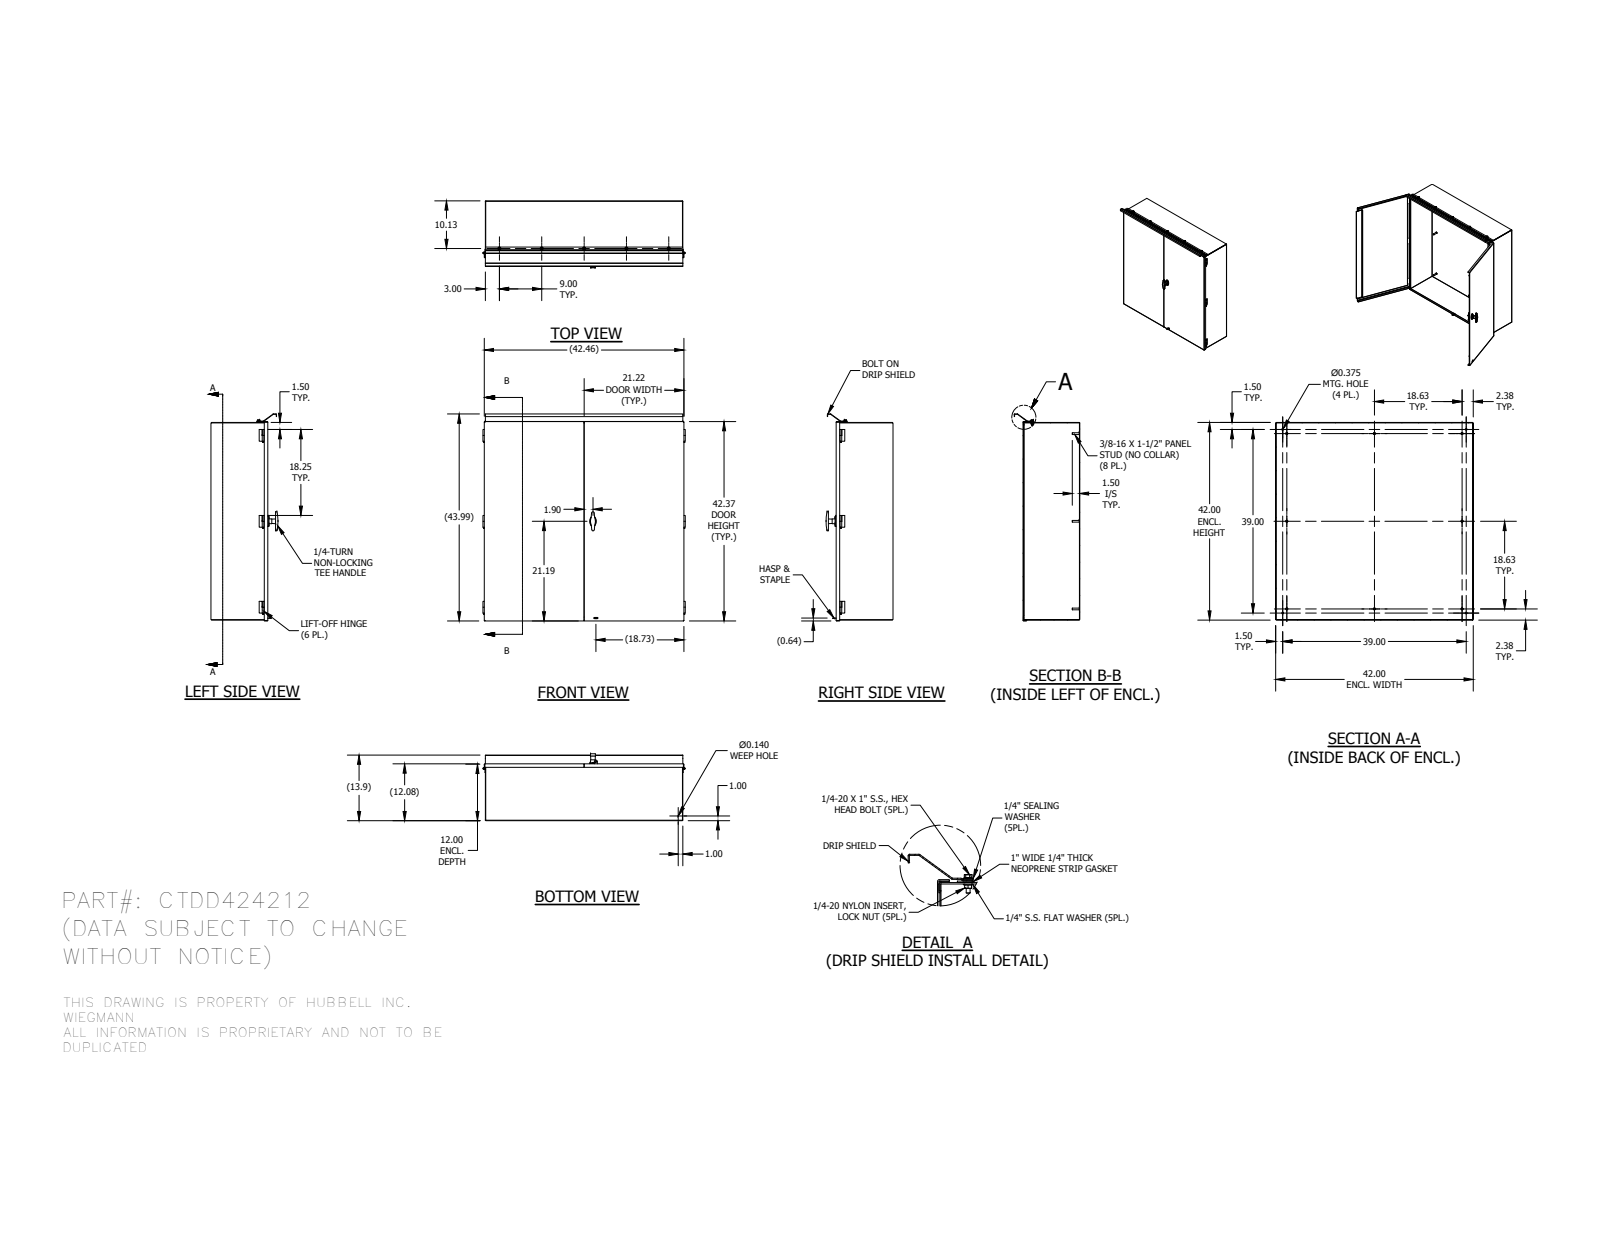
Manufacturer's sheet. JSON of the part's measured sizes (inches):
{"part_name": "CTDD424212BLR; CTDD4212TOP; CTDD4212BTM; 38822 (+8 more)", "step_written_by": "Autodesk Inventor 2014 (AUTOMOTIVE_DESIGN)", "units": "inches", "bodies": {"solids": 71, "faces": 1163, "planar": 669, "cylindrical": 242, "other": 252}, "overall_size": [43.995, 43, 14.235], "volume_in3": 597.4, "surface_area_in2": 12840, "round_holes": [[0.196, 7], [0.281, 7], [0.235, 5], [0.275, 5], [0.29, 5], [0.375, 5], [0.16, 2], [0.211, 2], [0.219, 2], [0.25, 2], [0.281, 2], [0.094, 1]], "round_bosses_or_shafts": [[0.462, 8], [0.375, 8], [0.438, 7], [0.25, 7], [0.65, 5], [0.625, 5], [0.6, 5], [0.26, 5]], "partial_cylinders_radius": [[0.031, 23], [0.125, 13], [0.105, 6], [0.125, 6], [0.063, 3], [0.063, 3], [0.008, 2], [0.156, 2]], "face_to_face_distances": [0.094, 11.984, 41.906, 11.891, 12.078, 0.093, 42, 41.813, 42, 41.813], "hole_center_spacings": [9, 39, 18, 0.75, 25.726, 26.277, 26.839, 27]}
